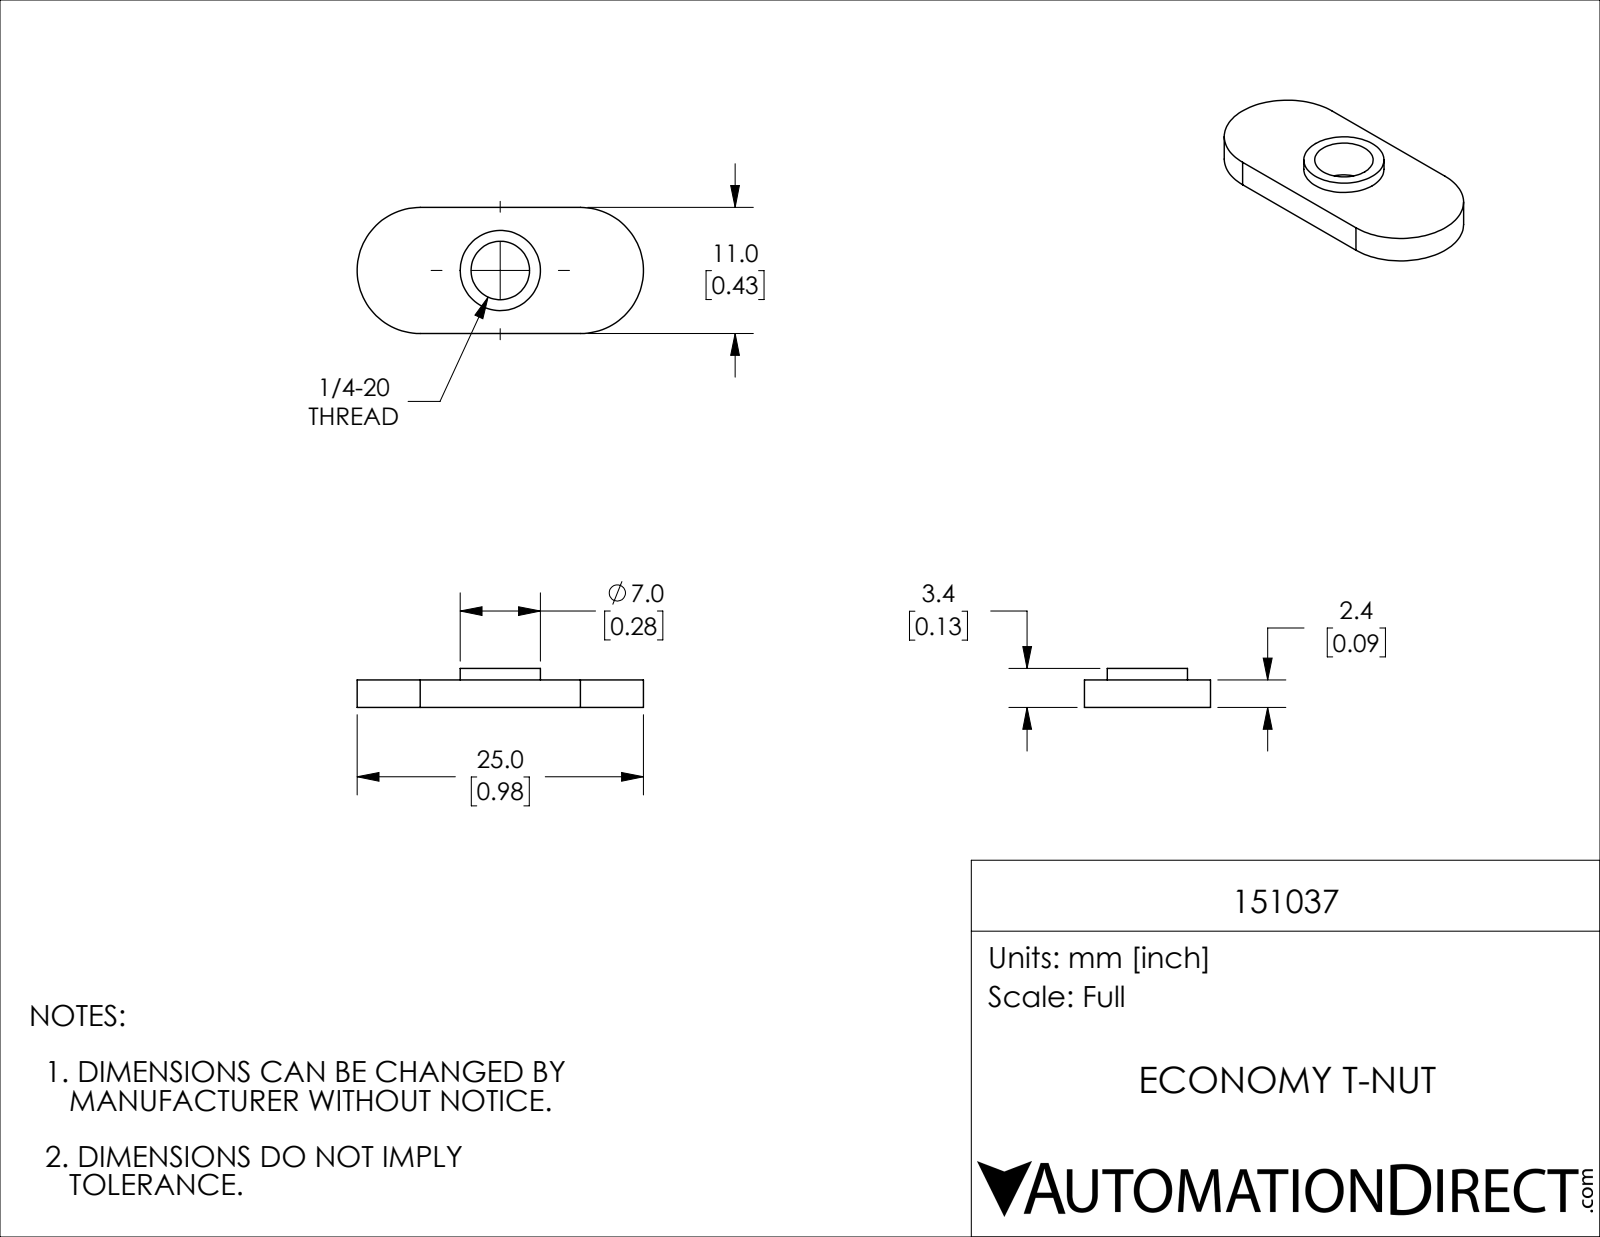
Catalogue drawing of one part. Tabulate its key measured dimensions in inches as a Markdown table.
| quantity | value |
| --- | --- |
| part name | 151037 |
| STEP written by | SolidWorks 2021 (CONFIG_CONTROL_DESIGN) |
| units | inches |
| bodies | 1 solid, 12 faces (5 planar, 7 cylindrical, 0 other) |
| overall size | 0.984 × 0.433 × 0.134 |
| volume | 0.035 in³ |
| surface area | 1.06 in² |
| round holes (diameter × count) | 0.201 × 1 |
| round bosses / shafts (diameter × count) | 0.276 × 1 |
| partial cylindrical surfaces (radius × count) | 0.217 × 2 |
| main face-to-face distances | 0.094, 0.433, 0.039, 0.134 |
